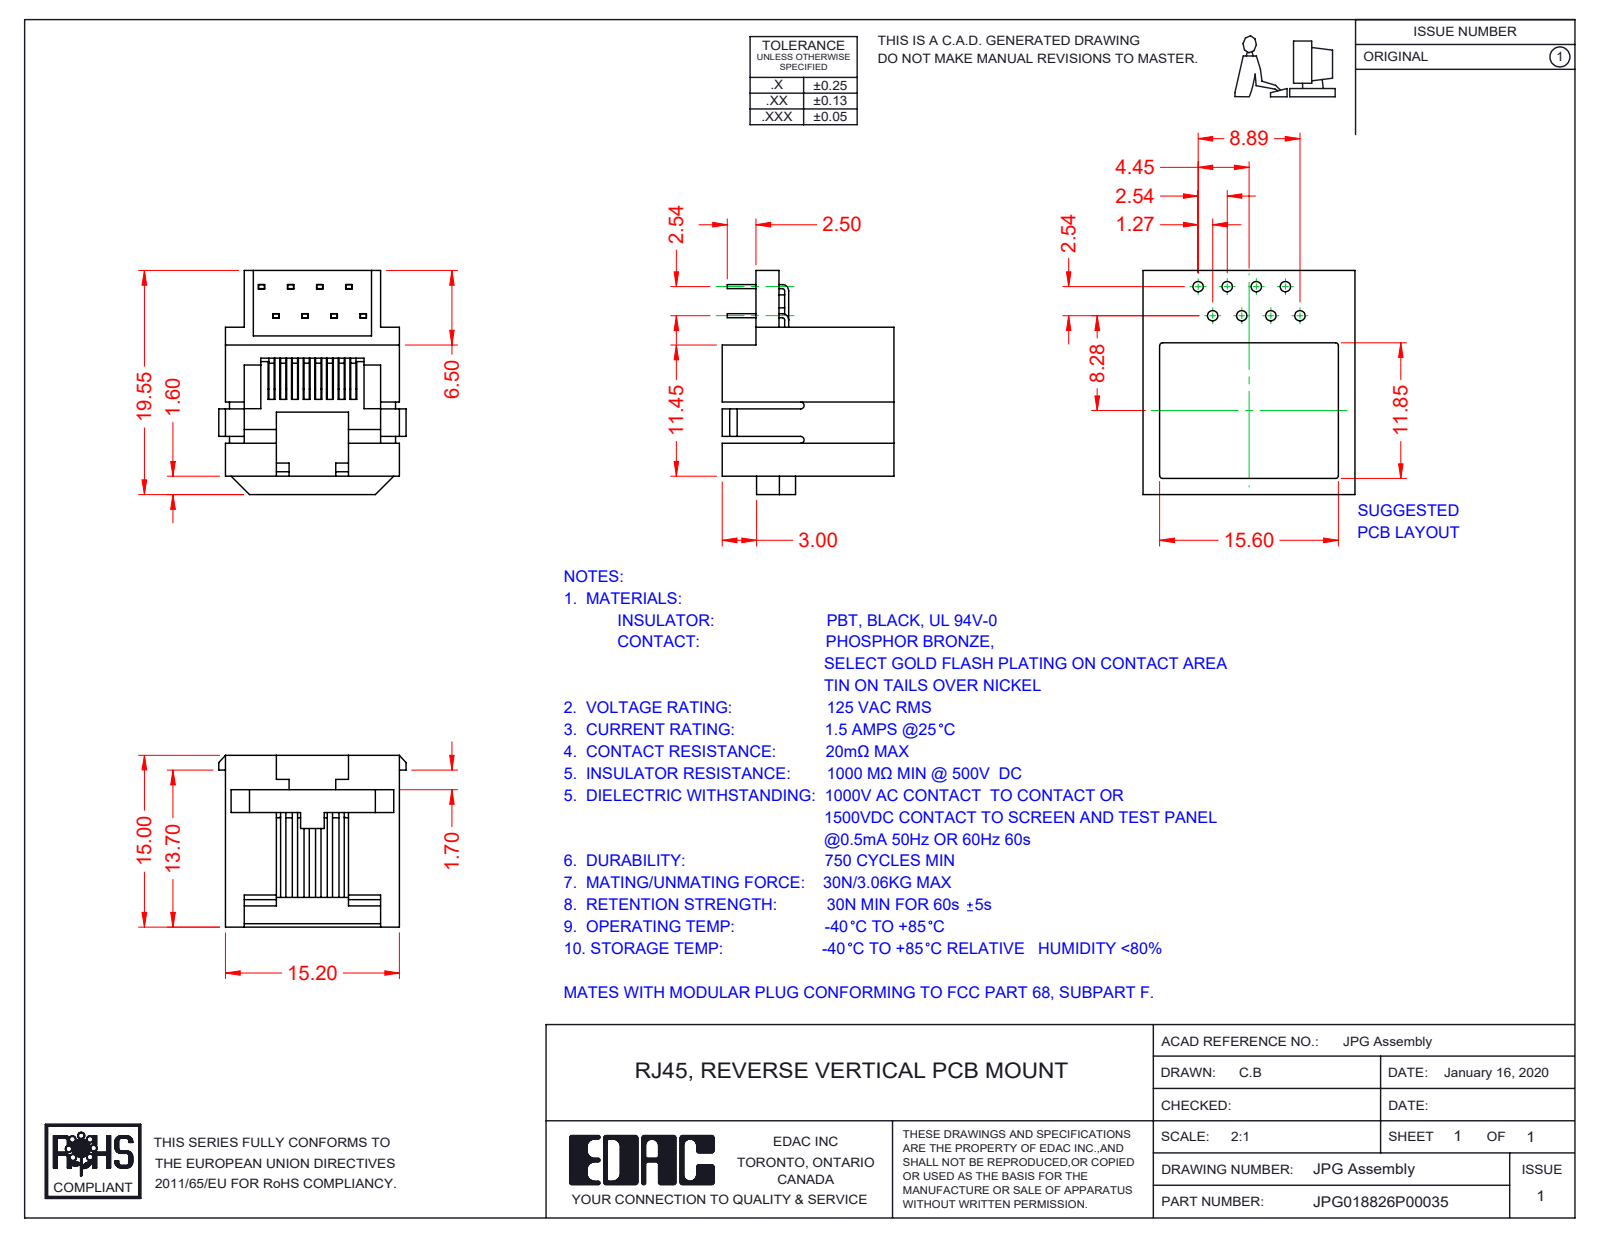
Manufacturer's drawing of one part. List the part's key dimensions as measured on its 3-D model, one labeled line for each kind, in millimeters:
Part name (STEP PRODUCT): PG Contacts; JPG018826P00035; PG Contact Lock; PG Insulator
STEP written by: SolidWorks 2016 (CONFIG_CONTROL_DESIGN)
Units: millimetres
Bodies: 10 solids, 542 faces (461 planar, 69 cylindrical, 12 other)
Overall size (bounding box): 19.55 × 16.35 × 15
Volume: 1 392 mm³ · Surface area: 2 707 mm²
Partial cylindrical surfaces — rounded edges, fillets, slot ends (radius × count): R0.3 ×3, R0.2 ×2, R0.35 ×2, R0.55 ×2, R0.7 ×2
Main face-to-face distances: 0.35, 1.64, 13.56, 10.3, 15.2, 2.6, 1.8, 0.6, 1.35, 12.9
